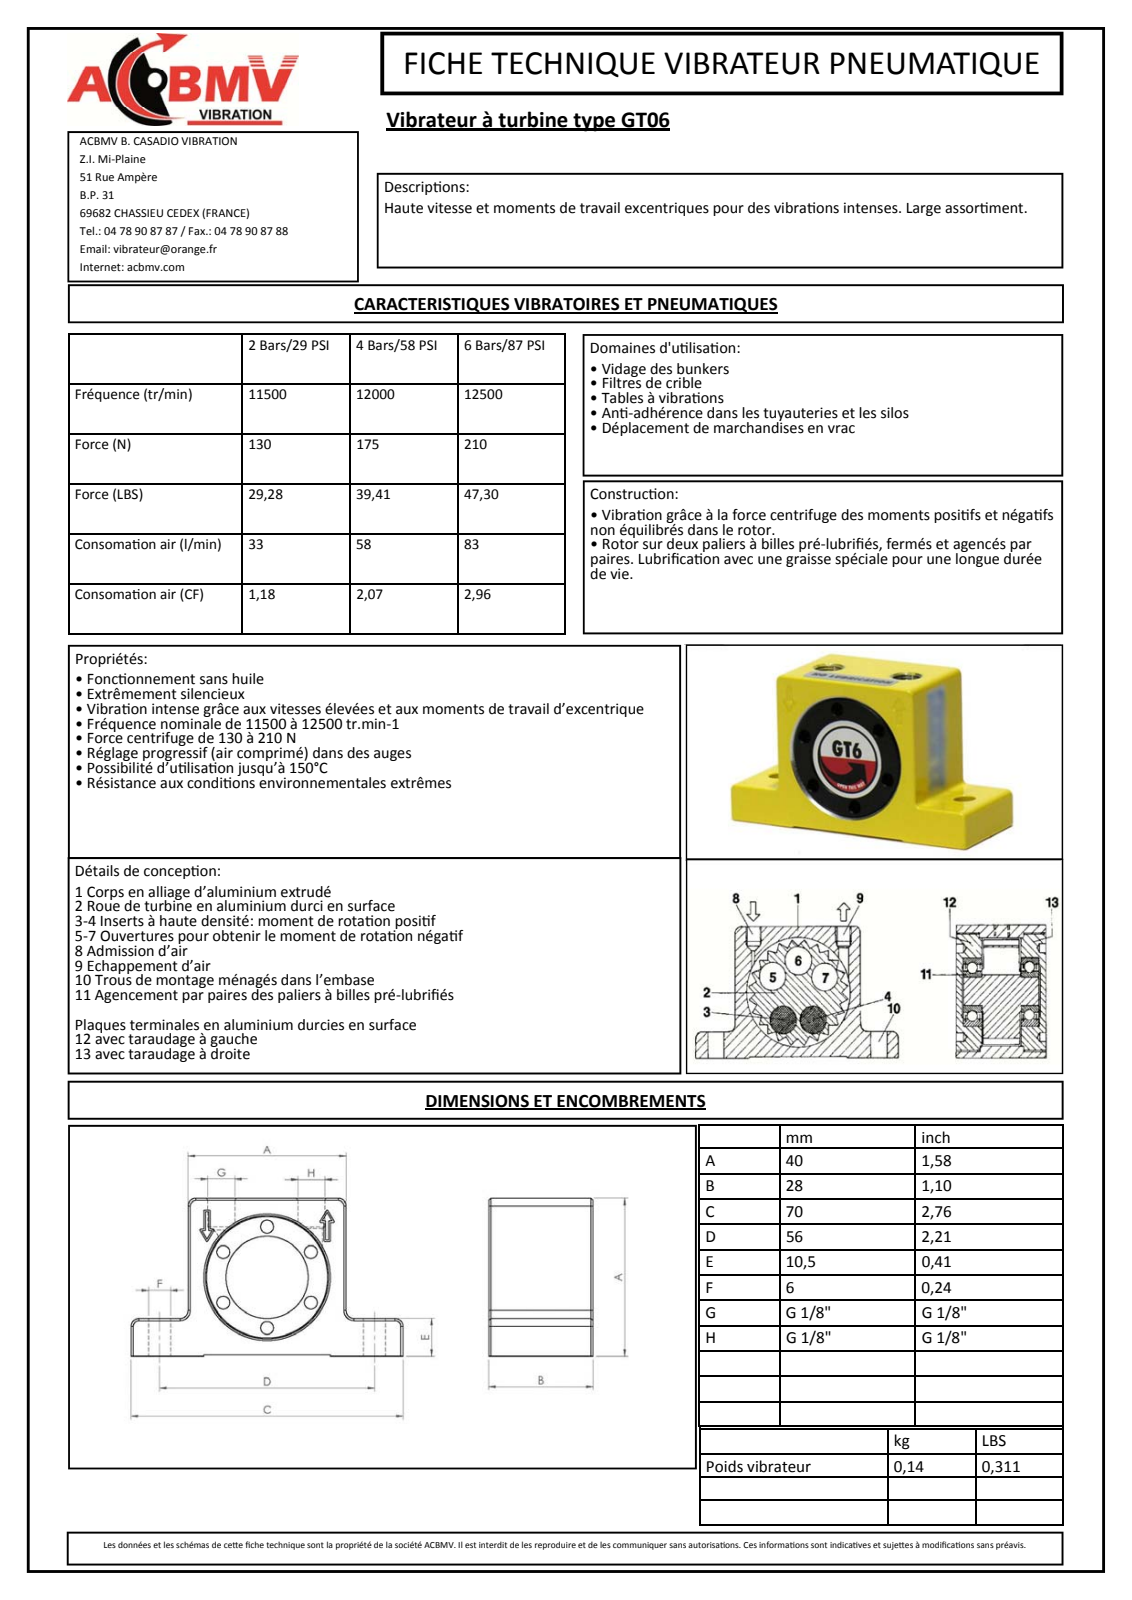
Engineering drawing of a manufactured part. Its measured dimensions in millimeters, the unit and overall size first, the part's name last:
Units: millimetres
Overall size (bounding box): 70 × 40 × 28
Round holes (diameter × count): ⌀4.1 ×6, ⌀6 ×2, ⌀8.57 ×2, ⌀1.79 ×1, ⌀17 ×1
Round bosses / shafts (diameter × count): ⌀1.61 ×1
Partial cylindrical surfaces — rounded edges, fillets, slot ends (radius × count): R0.2 ×14, R2 ×6, R0.46 ×4, R0.31 ×3, R0.54 ×3, R0.62 ×3, R1.24 ×3, R0.23 ×2
Main face-to-face distances: 40, 0.5, 28, 39.5, 10, 9.5, 30, 15, 55, 27.9
Hole centre spacings: 12, 20.78, 24, 16, 40, 9.87, 16.98, 27.76
Volume: 50 592 mm³ · Surface area: 10 731 mm²
Bodies: 1 solid, 254 faces (164 planar, 63 cylindrical, 27 other)
Part name (STEP PRODUCT): 8006-00-M
STEP written by: Autodesk Inventor 2011 (CONFIG_CONTROL_DESIGN)
